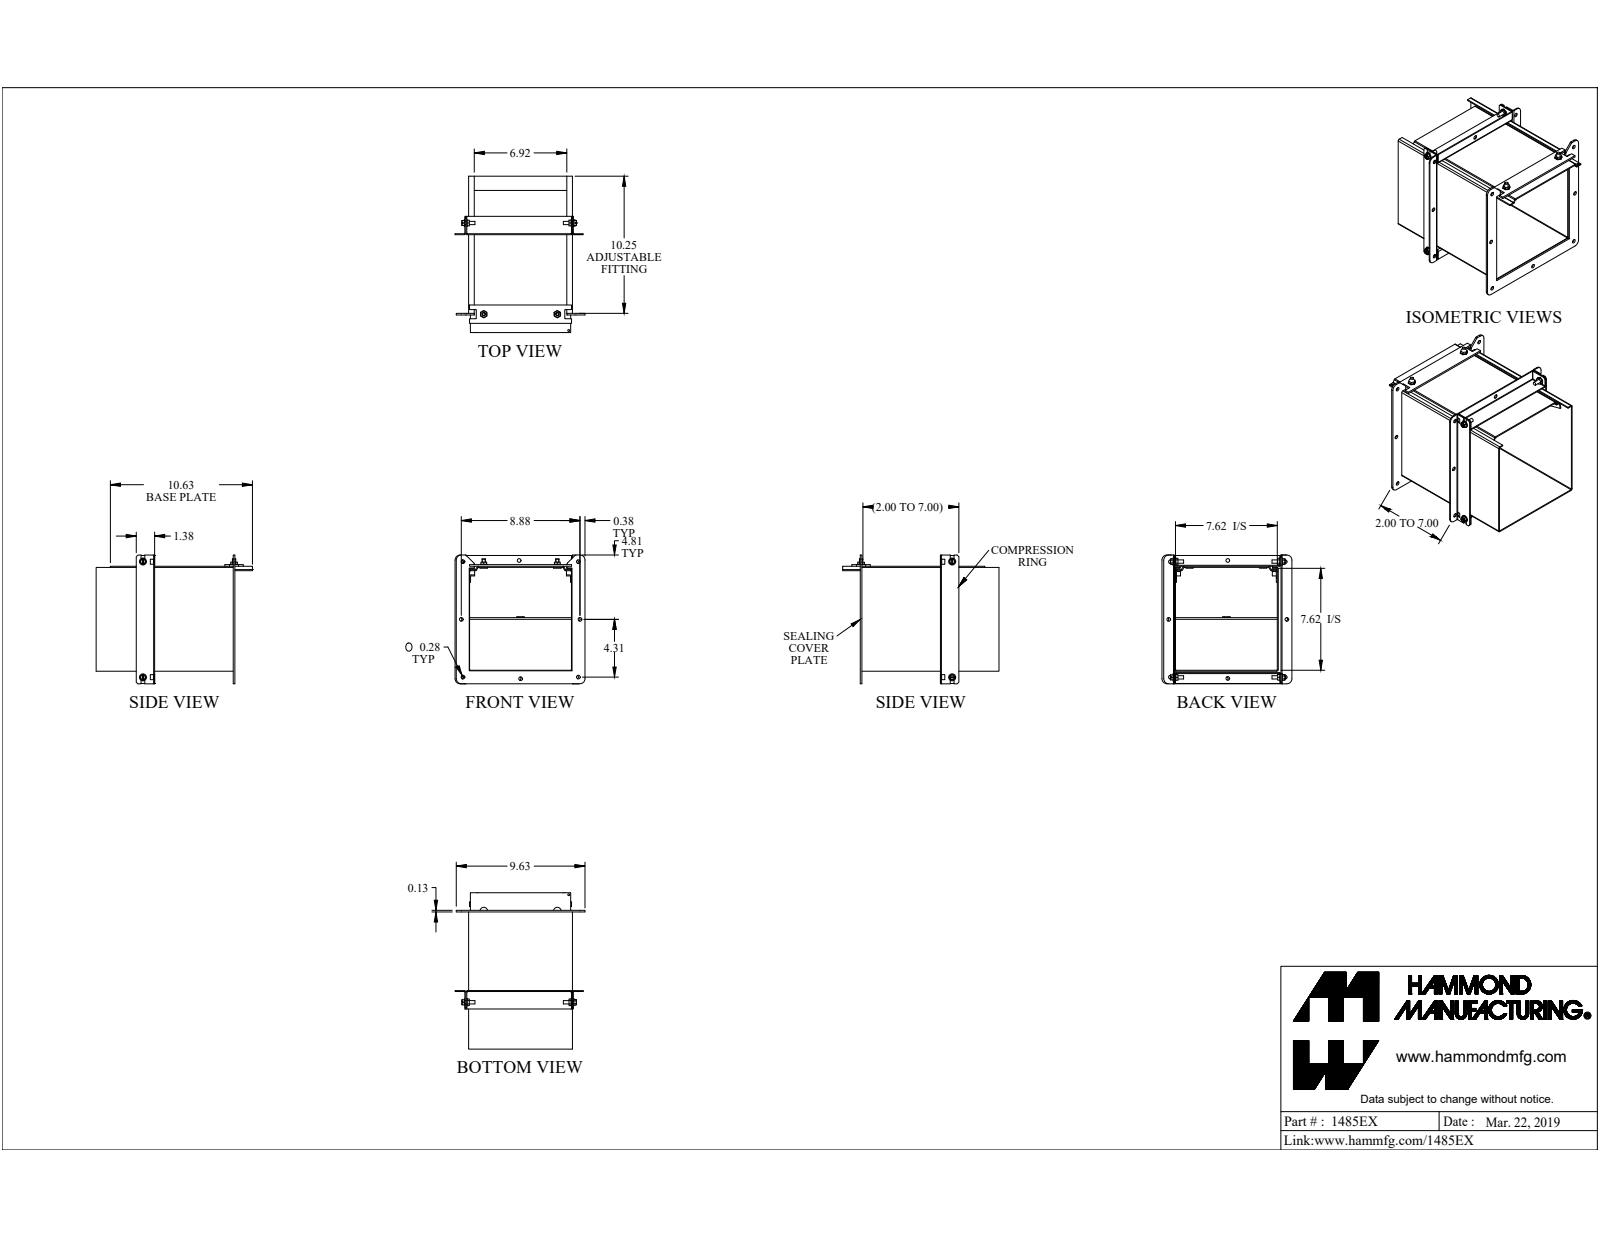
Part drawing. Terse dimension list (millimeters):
name: 1485EX
written by: SolidWorks 2019 (CONFIG_CONTROL_DESIGN)
unit: mm
bodies: 22 solids, 467 faces (330 planar, 103 cylindrical, 34 other)
size: 296.9 × 246.8 × 244.6
volume: 567 300 mm³; area: 590 100 mm²
holes: 17× ⌀7.1, 5× ⌀5, 3× ⌀8.9, 2× ⌀3.6, 2× ⌀6.7, 2× ⌀8
bosses: 3× ⌀6.2, 2× ⌀14.3, 2× ⌀13.2, 2× ⌀6.4
rounds: 14× R0.9, 14× R2.7, 8× R9.5, 4× R0.1, 4× R2.2, 4× R3.2, 2× R3.6
face distances: 1.8, 195.3, 197.1, 199.2, 193.4, 2.1, 197.4, 197.2, 195.3, 3.2
hole spacings: 109.6, 246.9, 247.8, 219.1, 2.4, 3.4, 106.7, 109.1
